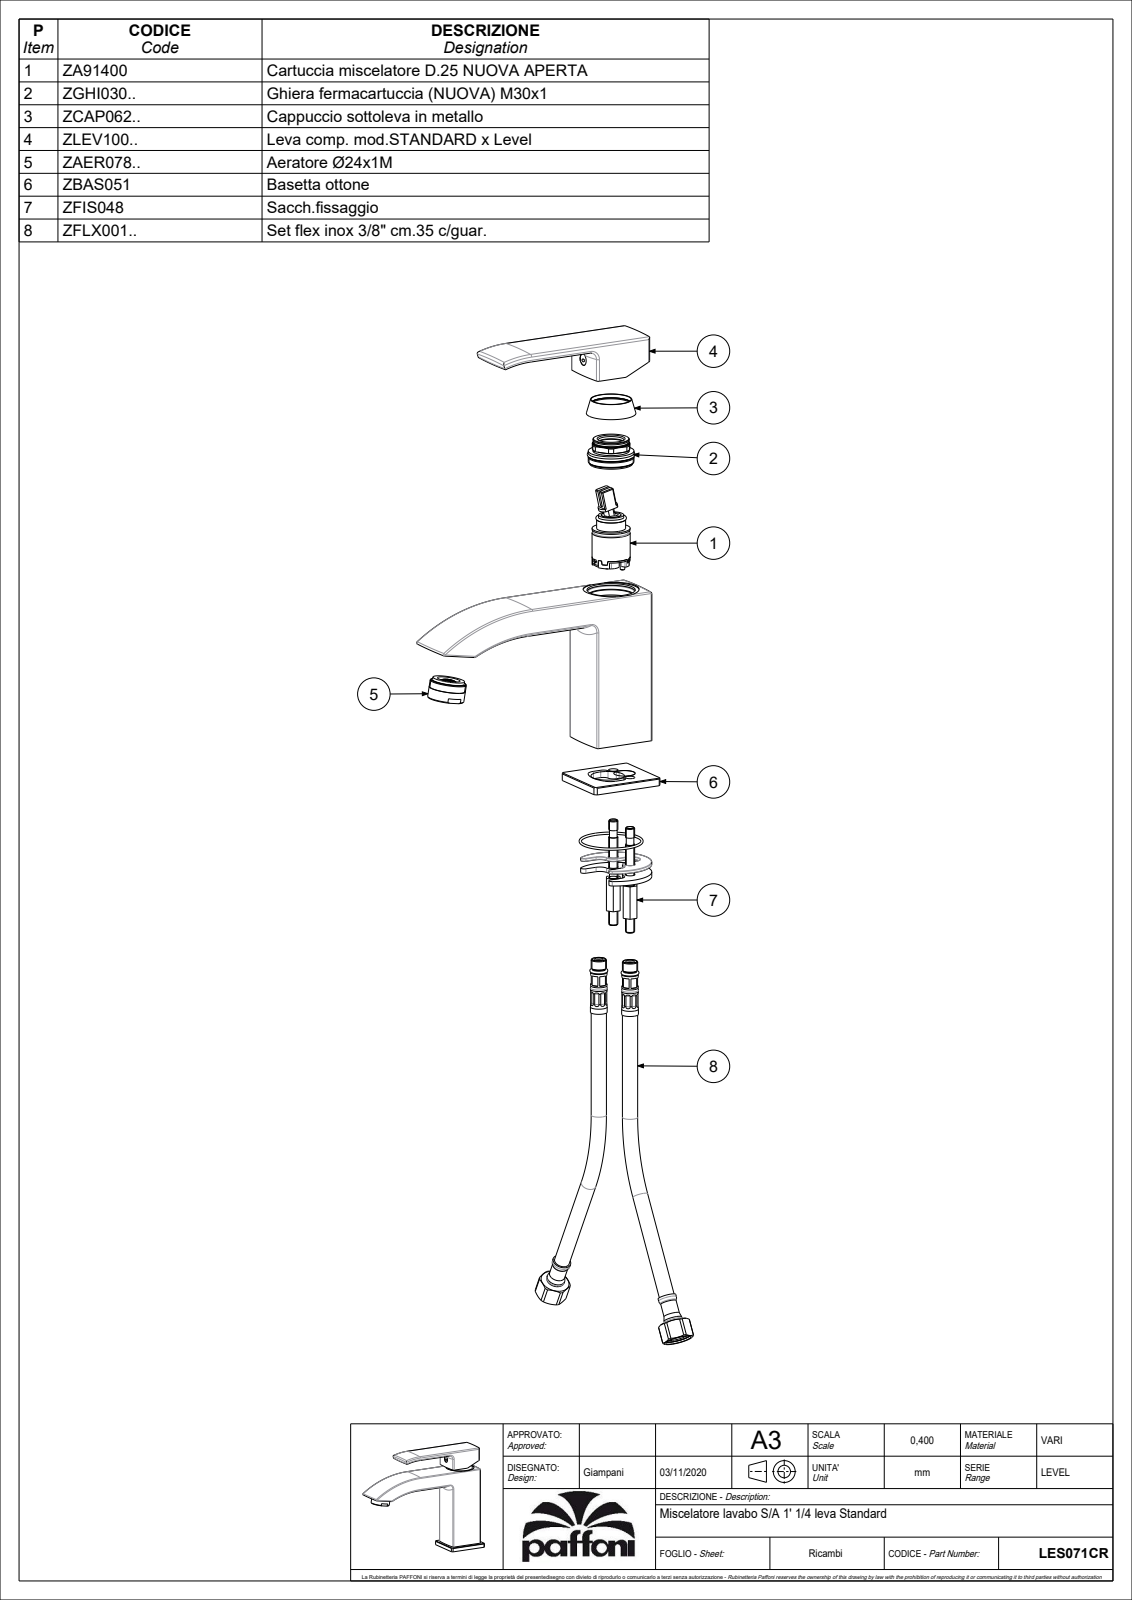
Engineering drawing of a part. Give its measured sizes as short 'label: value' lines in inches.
name: LES071CR
written by: CREO PARAMETRIC BY PTC INC, 2020044 (CONFIG_CONTROL_DESIGN)
unit: in
bodies: 2 solids, 2622 faces (1721 planar, 479 cylindrical, 422 other)
size: 6.411 × 5.316 × 1.772
volume: 10.04 in³; area: 142.6 in²
holes: 2× ⌀0.138, 2× ⌀0.197, 2× ⌀0.207, 2× ⌀0.244, 2× ⌀0.354, 2× ⌀0.433, 1× ⌀0.118, 1× ⌀0.217, 1× ⌀0.307, 1× ⌀0.63, 1× ⌀0.657, 1× ⌀0.669
bosses: 2× ⌀0.118, 1× ⌀1.528, 1× ⌀1.24, 1× ⌀1.201, 1× ⌀1.181, 1× ⌀0.984, 1× ⌀0.945, 1× ⌀0.937
rounds: 78× R0.02, 53× R0.039, 16× R0.079, 12× R0.012, 10× R0.028, 9× R0.059, 8× R0.01, 8× R0.118
face distances: 0.118, 1.319, 1.437, 1.201, 0.03, 0.089, 1.289, 1.407, 0.197, 0.039
hole spacings: 0.355, 0.109, 0.197, 0.265, 0.352, 0.367, 0.482, 0.53
